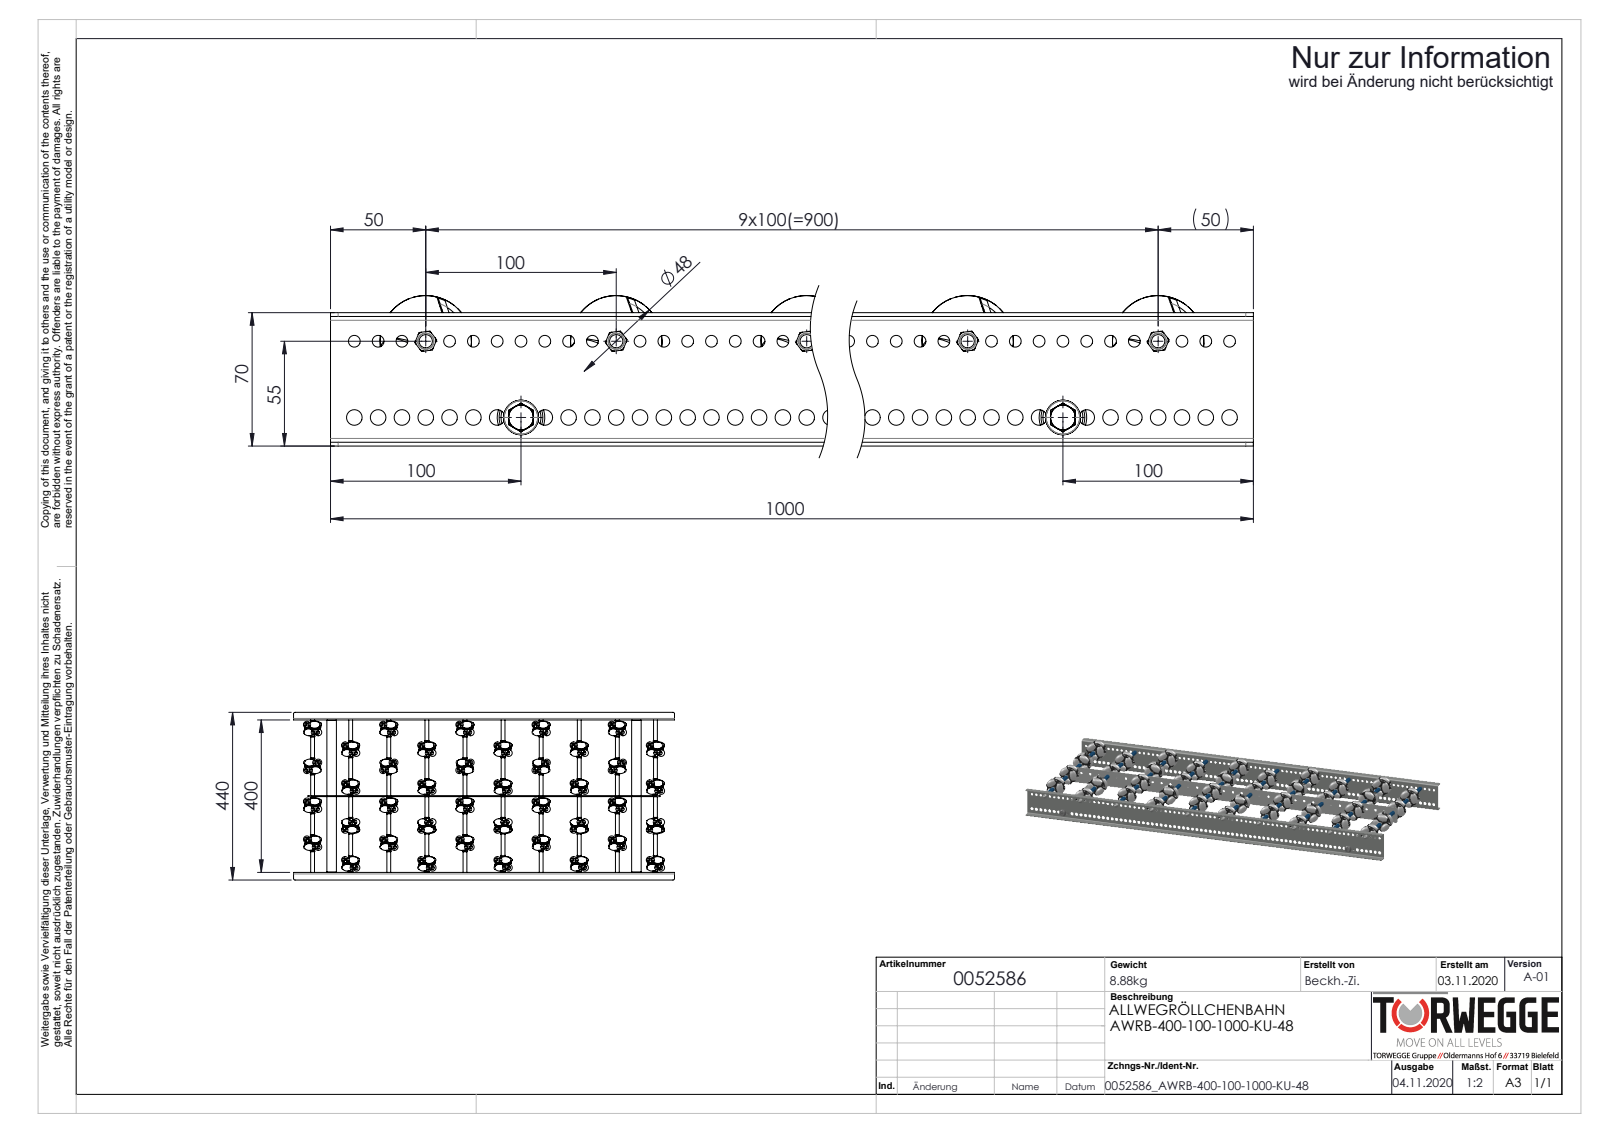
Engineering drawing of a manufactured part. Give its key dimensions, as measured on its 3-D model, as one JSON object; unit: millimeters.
{"part_name": "0052586; AWR48_Stift; AWR48_Halter; S108767_Längstraverse-42x2,5-AWR_L975 (+8 more)", "step_written_by": "SolidWorks 2020 (AUTOMOTIVE_DESIGN)", "units": "millimeters", "bodies": {"solids": 683, "faces": 12536, "planar": 4226, "cylindrical": 5026, "other": 3284}, "overall_size": [1000, 440, 78.99], "volume_mm3": 2549000, "surface_area_mm2": 1833000, "round_holes": [[3.7, 240], [4.2, 240], [6.2, 79], [8.2, 79], [6.5, 37], [4.92, 10], [8.4, 10], [6.8, 2], [21, 2]], "round_bosses_or_shafts": [[4, 240], [3.7, 202], [8, 12], [42, 10], [11, 10], [10, 10], [7, 10], [6, 10]], "partial_cylinders_radius": [[23.55, 10], [4, 8], [2, 4], [5, 4]], "face_to_face_distances": [2, 402, 68, 400, 404, 200.6, 198.6, 201.4, 203.4, 203.1], "hole_center_spacings": [36.06, 36.05, 36.07, 100, 36.04, 12.5, 200, 25]}
